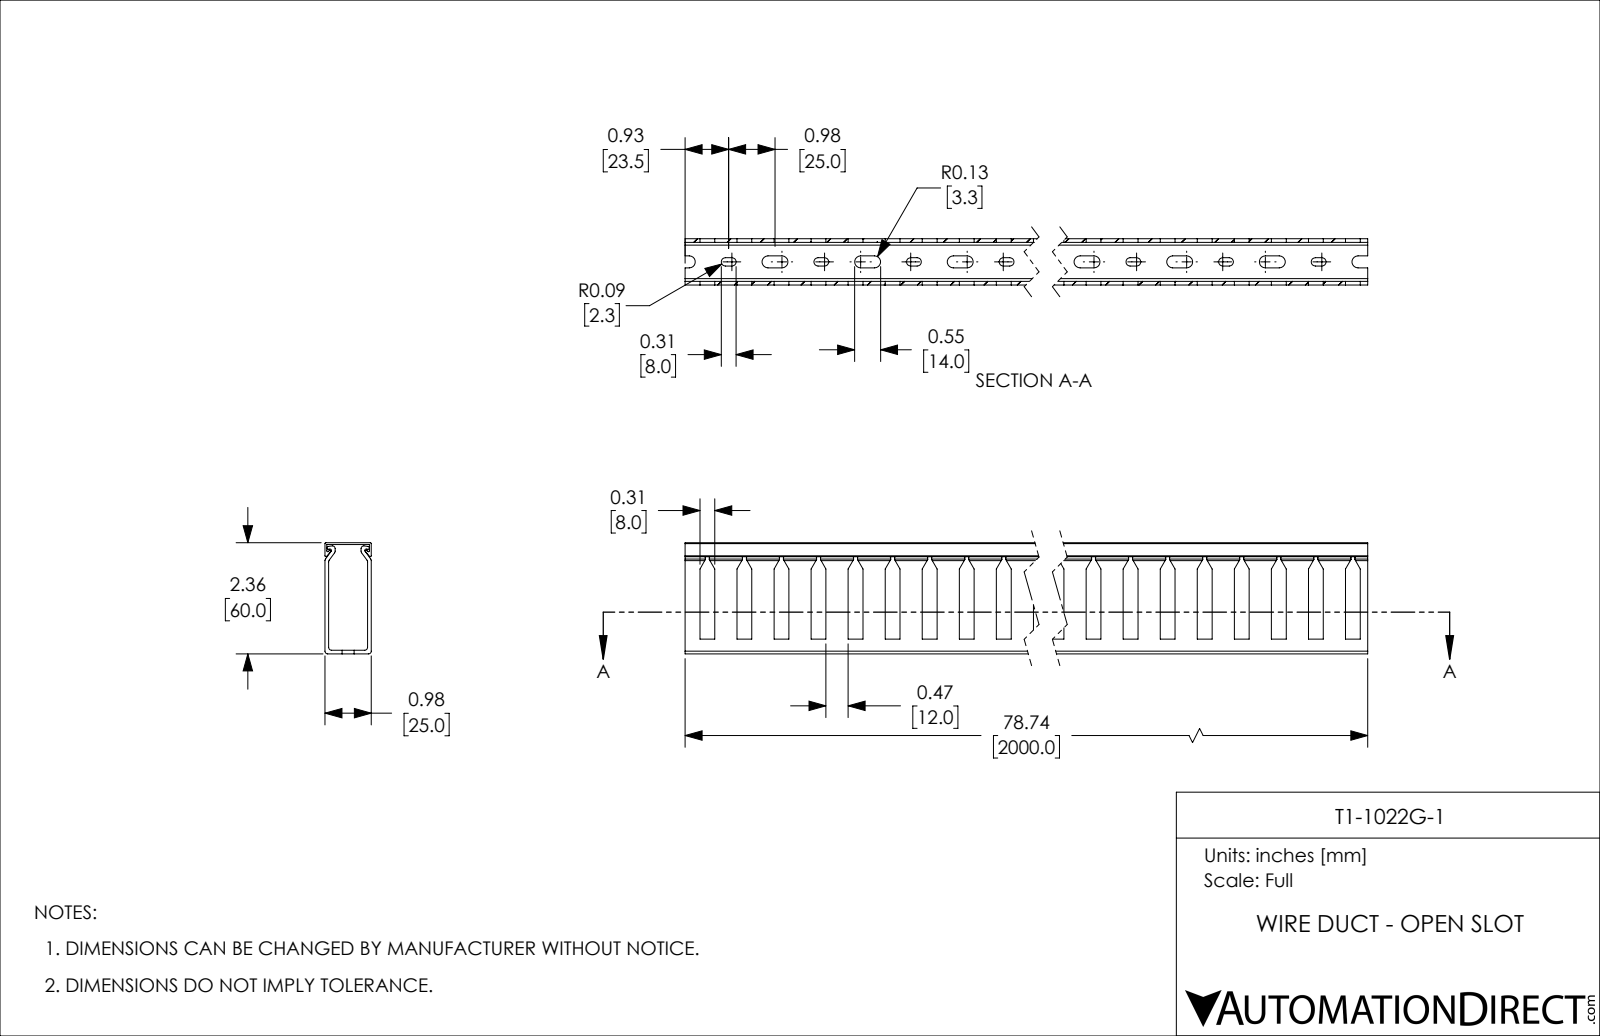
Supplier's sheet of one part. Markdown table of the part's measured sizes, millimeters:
| quantity | value |
| --- | --- |
| part name | T1-1022W-1 |
| STEP written by | SolidWorks 2021 (CONFIG_CONTROL_DESIGN) |
| units | millimeters |
| bodies | 2 solids, 945 faces (514 planar, 431 cylindrical, 0 other) |
| overall size | 2000 × 60 × 25 |
| volume | 636 380 mm³ |
| surface area | 728 302 mm² |
| partial cylindrical surfaces (radius × count) | 2.25 × 80, 3.25 × 80, 1.5 × 12, 0.5 × 8, 0.75 × 6 |
| main face-to-face distances | 2, 23, 25, 21, 1, 60, 59, 57, 58, 24 |
